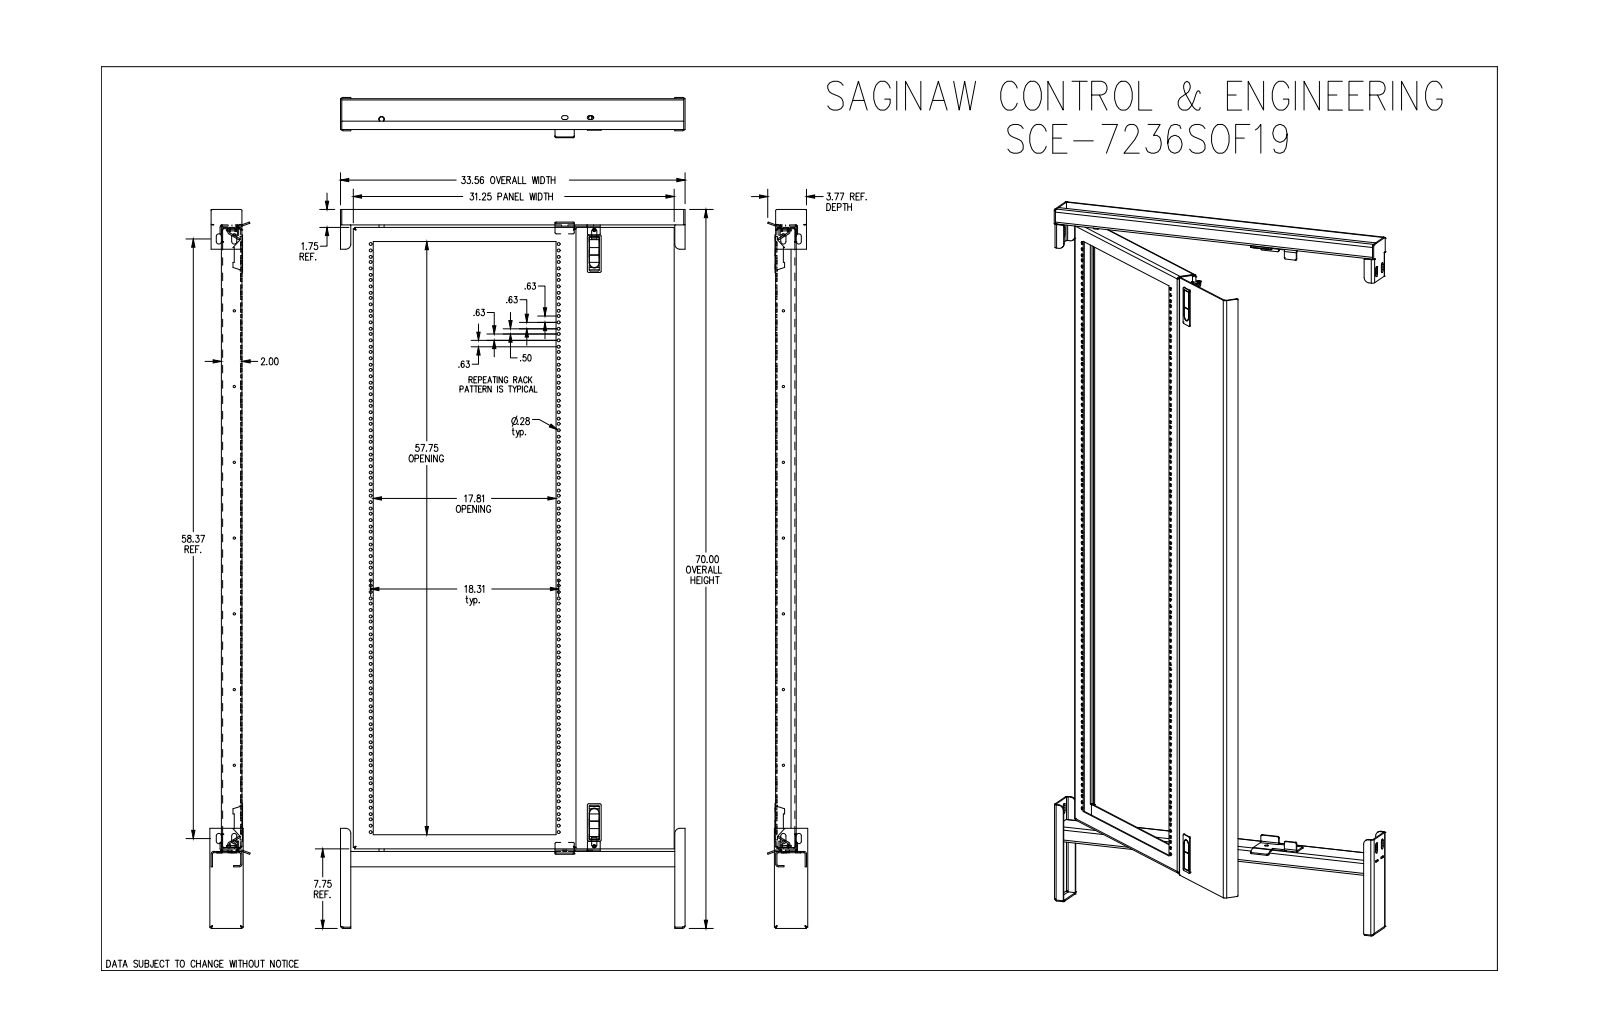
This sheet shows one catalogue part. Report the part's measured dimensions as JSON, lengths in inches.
{"part_name": "SCE-7236SOF19", "step_written_by": "SolidWorks 2019 (AUTOMOTIVE_DESIGN)", "units": "inches", "bodies": {"solids": 23, "faces": 1023, "planar": 573, "cylindrical": 421, "other": 29}, "overall_size": [69.996, 33.562, 3.92], "volume_in3": 249.8, "surface_area_in2": 4100, "round_holes": [[0.288, 138], [0.281, 60], [0.193, 9], [0.375, 2], [0.375, 2], [0.503, 1], [0.531, 1]], "round_bosses_or_shafts": [[0.256, 9], [0.188, 9], [0.16, 2], [0.5, 1]], "partial_cylinders_radius": [[0.125, 52], [0.25, 44], [0.125, 14], [0.031, 12], [0.062, 9], [0.02, 4], [0.15, 4], [0.187, 4]], "face_to_face_distances": [0.125, 0.125, 1.874, 21.563, 2.875, 61.118, 0.25, 9.437, 2, 3], "hole_center_spacings": [1.75, 3.5, 5.25, 7, 8.75, 10.5, 0.625, 0.625]}
